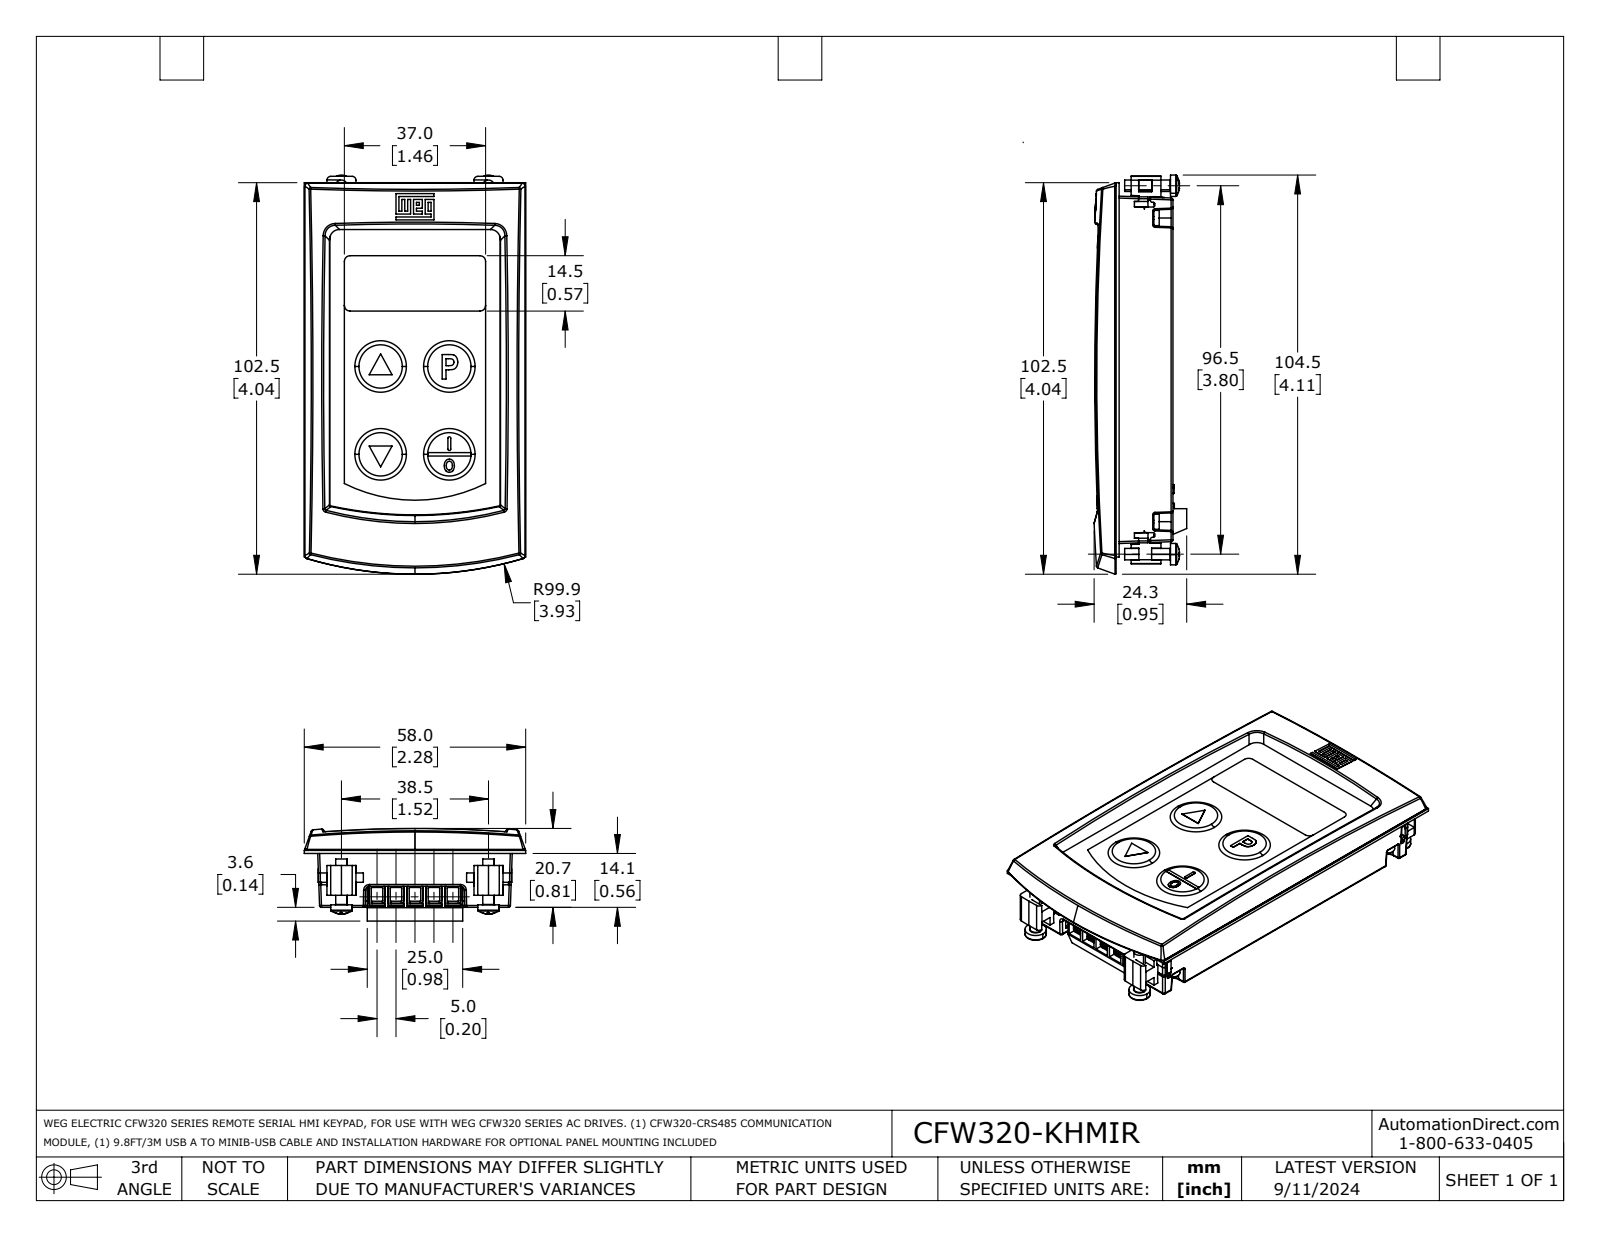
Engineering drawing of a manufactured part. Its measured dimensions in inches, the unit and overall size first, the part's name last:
Units: inches
Overall size (bounding box): 4.115 × 2.283 × 0.955
Round holes (diameter × count): ⌀0.15 ×5, ⌀0.094 ×2
Round bosses / shafts (diameter × count): ⌀0.22 ×4, ⌀0.157 ×4, ⌀0.118 ×4
Partial cylindrical surfaces — rounded edges, fillets, slot ends (radius × count): R0.012 ×169, R0.02 ×49, R0.008 ×43, R0.028 ×20, R2.523 ×20, R0.039 ×12, R0.387 ×8, R0.387 ×8
Main face-to-face distances: 0.014, 0.654, 0.667, 0.665, 0.679, 0.555, 0.124, 0.658, 0.646, 0.021
Hole centre spacings: 0.196, 0.391, 0.519, 0.587, 0.672, 0.842, 1.022, 1.207
Volume: 5.094 in³ · Surface area: 53.35 in²
Bodies: 5 solids, 2448 faces (929 planar, 659 cylindrical, 860 other)
Part name (STEP PRODUCT): CFW320-KHMIR
STEP written by: SolidWorks 2021 (AUTOMOTIVE_DESIGN)
